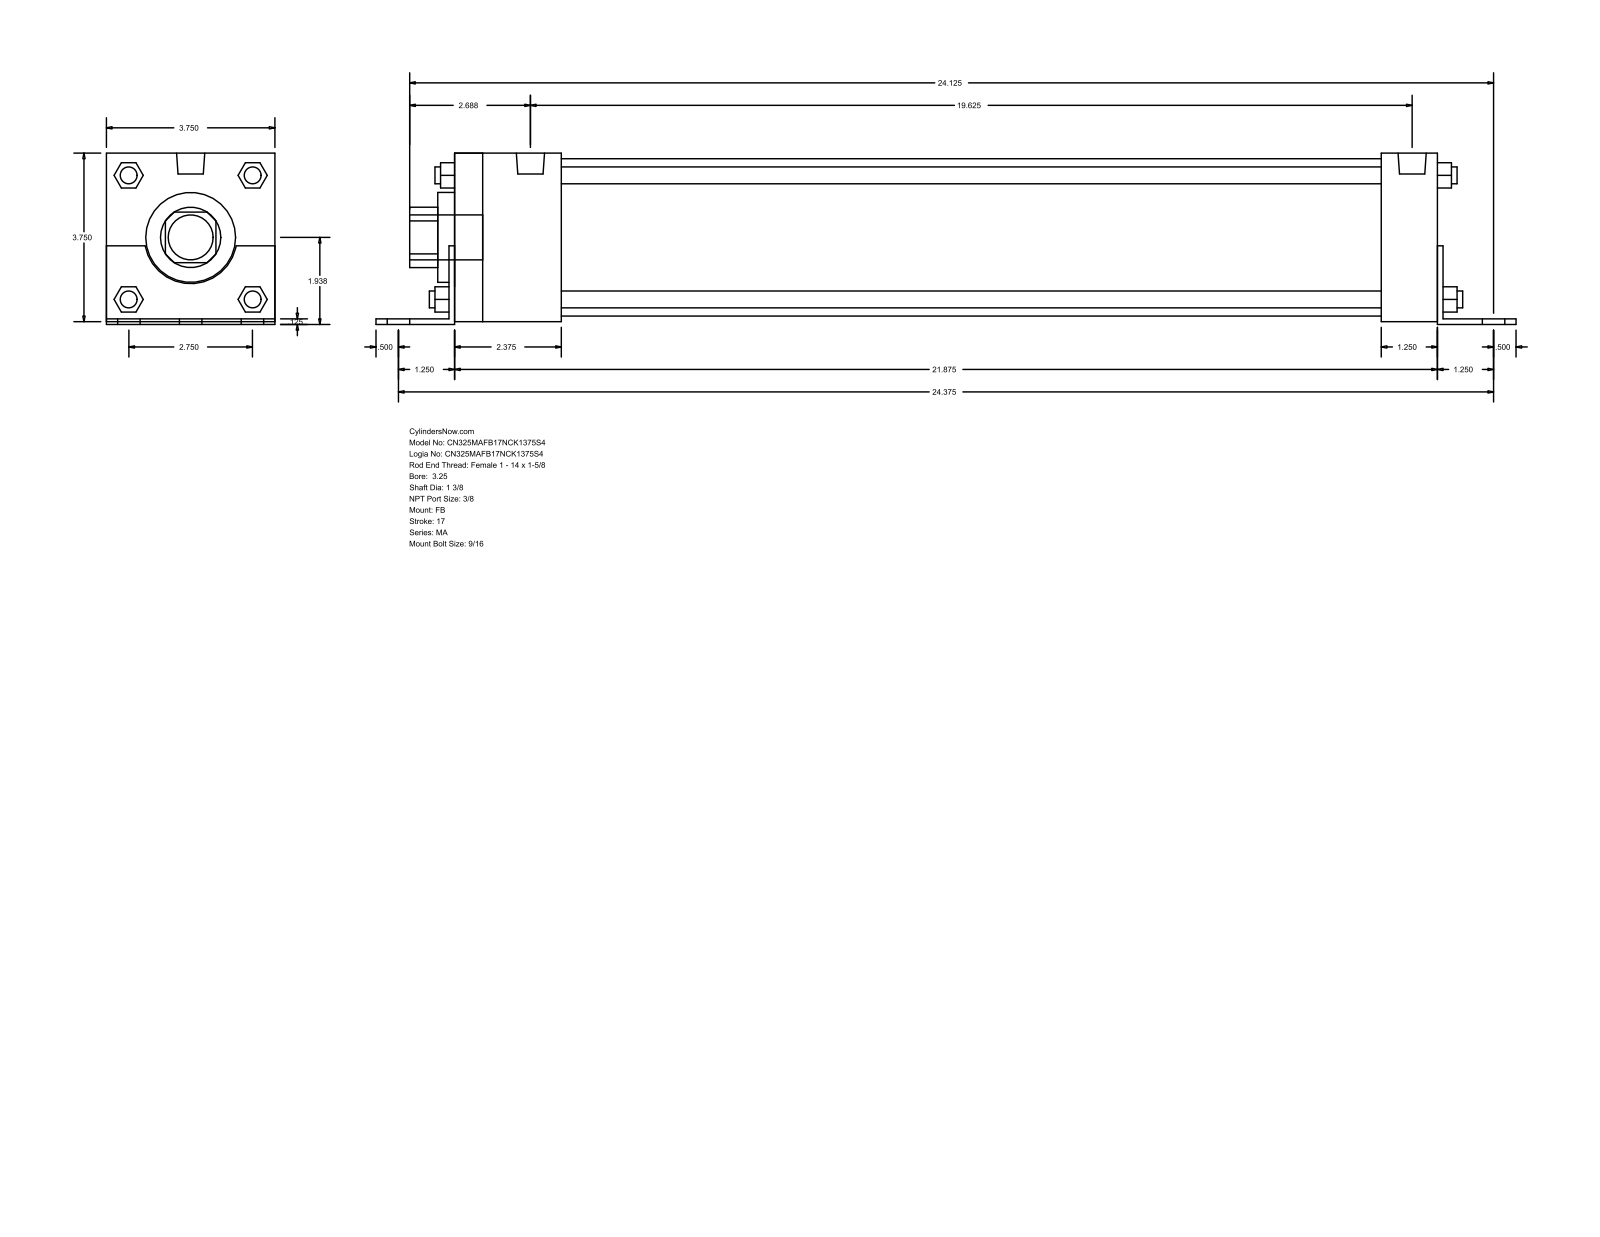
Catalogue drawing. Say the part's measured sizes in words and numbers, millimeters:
The part is named "MA_FB__0325_1.375". Its 3-D file was written by "GSSL Pune (CONFIG_CONTROL_DESIGN)". It is 0 solids with 140 faces: 105 planar, 35 cylindrical and 0 other. Overall it measures 644.52 by 96.84 by 95.25 millimeters. Round holes: 1 of diameter 34.92, 1 of diameter 50.8, 1 of diameter 88.9. Round bosses or shafts: 6 of diameter 14.29, 4 of diameter 11.11, 4 of diameter 9.53, 2 of diameter 15.93, 1 of diameter 25.4. Partial cylindrical surfaces (rounded edges, fillets, slot ends): 1 of radius 17.06, 1 of radius 26.16. The main face-to-face distances are 95.24, 3.17, 1.59, 96.83, 1.58, 93.66, 3.18, 555.62, 558.8, 31.75.
